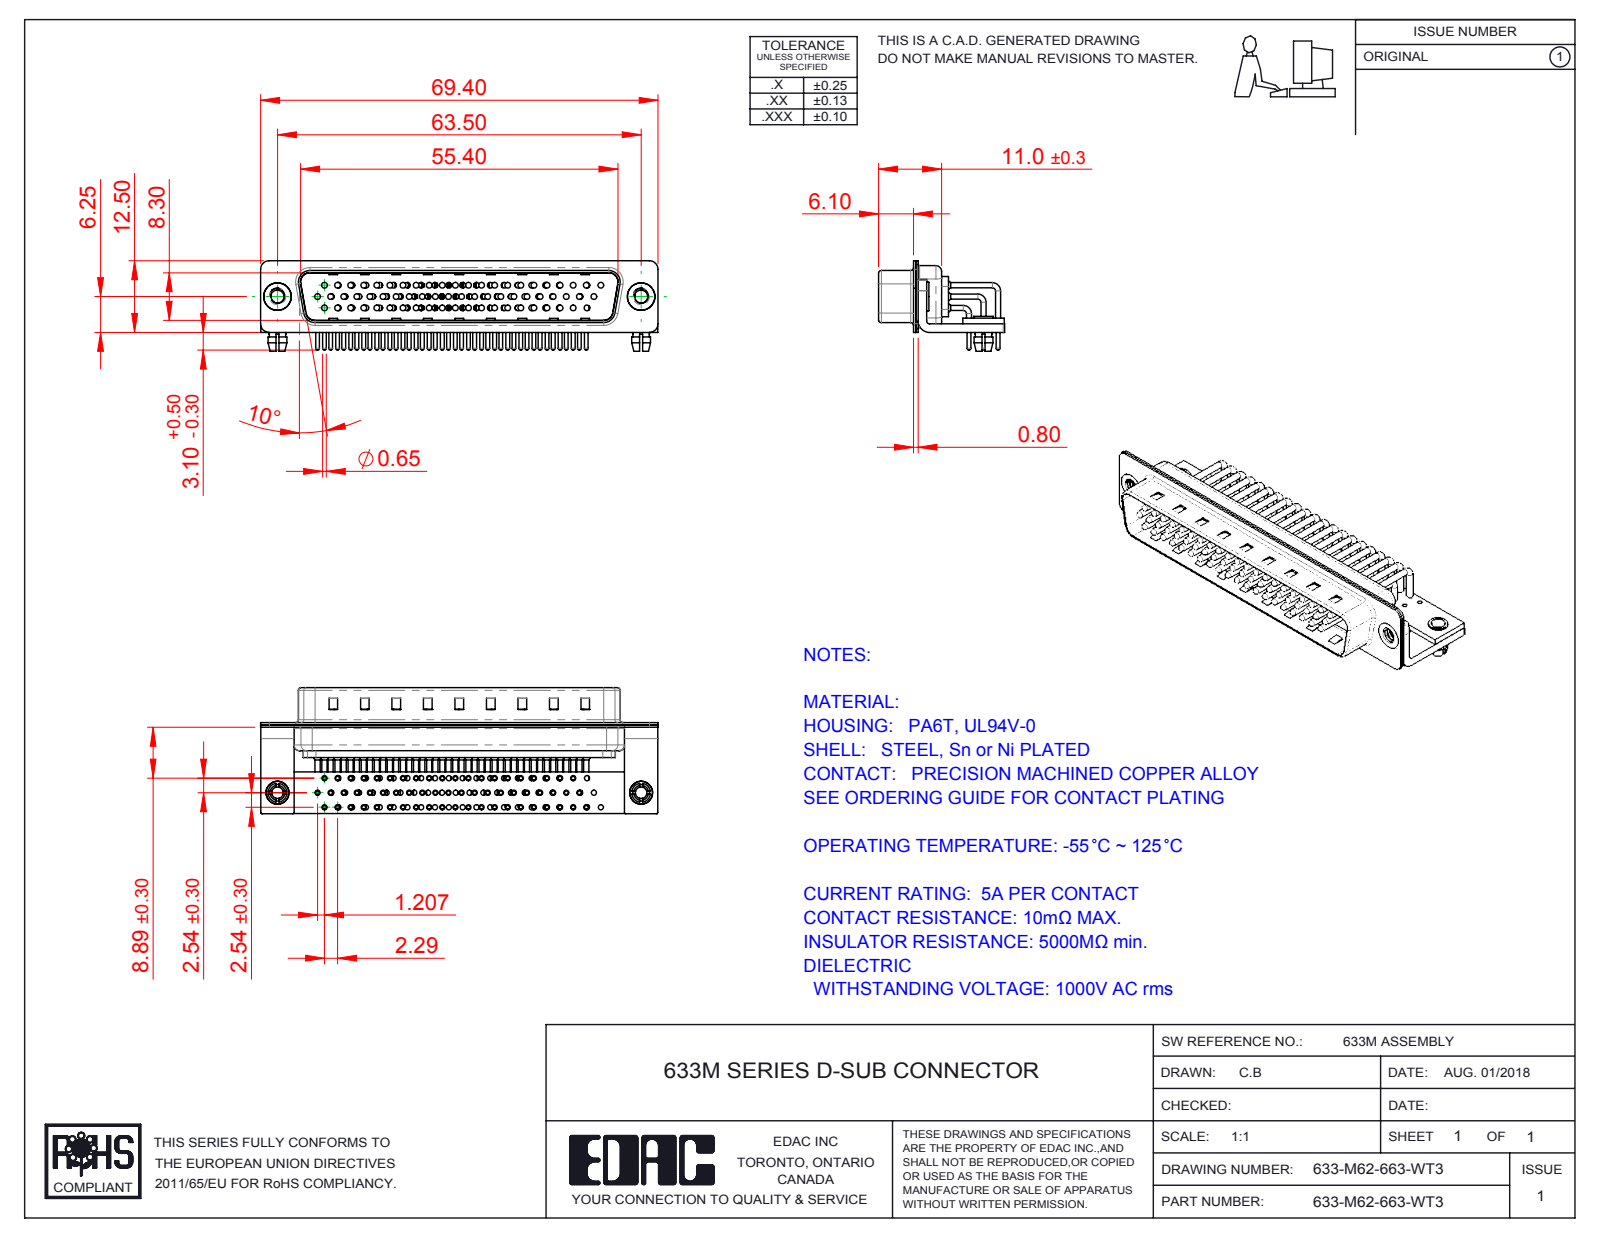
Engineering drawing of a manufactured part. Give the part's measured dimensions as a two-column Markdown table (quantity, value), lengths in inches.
| quantity | value |
| --- | --- |
| part name | 633M Shell Front_62 Contacts; 633M Contact Row 3; 633M 4-40 Threaded Rivet_Stabilizer; 633-M62-663-WT3 (+7 more) |
| STEP written by | SolidWorks 2016 (CONFIG_CONTROL_DESIGN) |
| units | inches |
| bodies | 72 solids, 7498 faces (4245 planar, 2551 cylindrical, 702 other) |
| overall size | 2.732 × 0.866 × 0.622 |
| volume | 0.312 in³ |
| surface area | 24.39 in² |
| round holes (diameter × count) | 0.079 × 64, 0.035 × 62, 0.039 × 62, 0.067 × 62, 0.089 × 2, 0.098 × 2, 0.126 × 2, 0.157 × 2, 0.189 × 2 |
| round bosses / shafts (diameter × count) | 0.035 × 118, 0.059 × 62, 0.026 × 62, 0.039 × 56, 0.197 × 2, 0.193 × 2, 0.157 × 2, 0.134 × 2 |
| partial cylindrical surfaces (radius × count) | 0.04 × 62, 0.01 × 16, 0.059 × 16, 0.079 × 13, 0.02 × 9, 0.063 × 8, 0.024 × 4, 0.026 × 4 |
| main face-to-face distances | 0.016, 0.033, 0.049, 0.059, 0.376, 0.039, 0.075, 0.409, 0.031, 0.327 |
| hole center spacings | 0.285, 0.095, 0.38, 0.19, 0.57, 0.665, 0.111, 0.091 |
